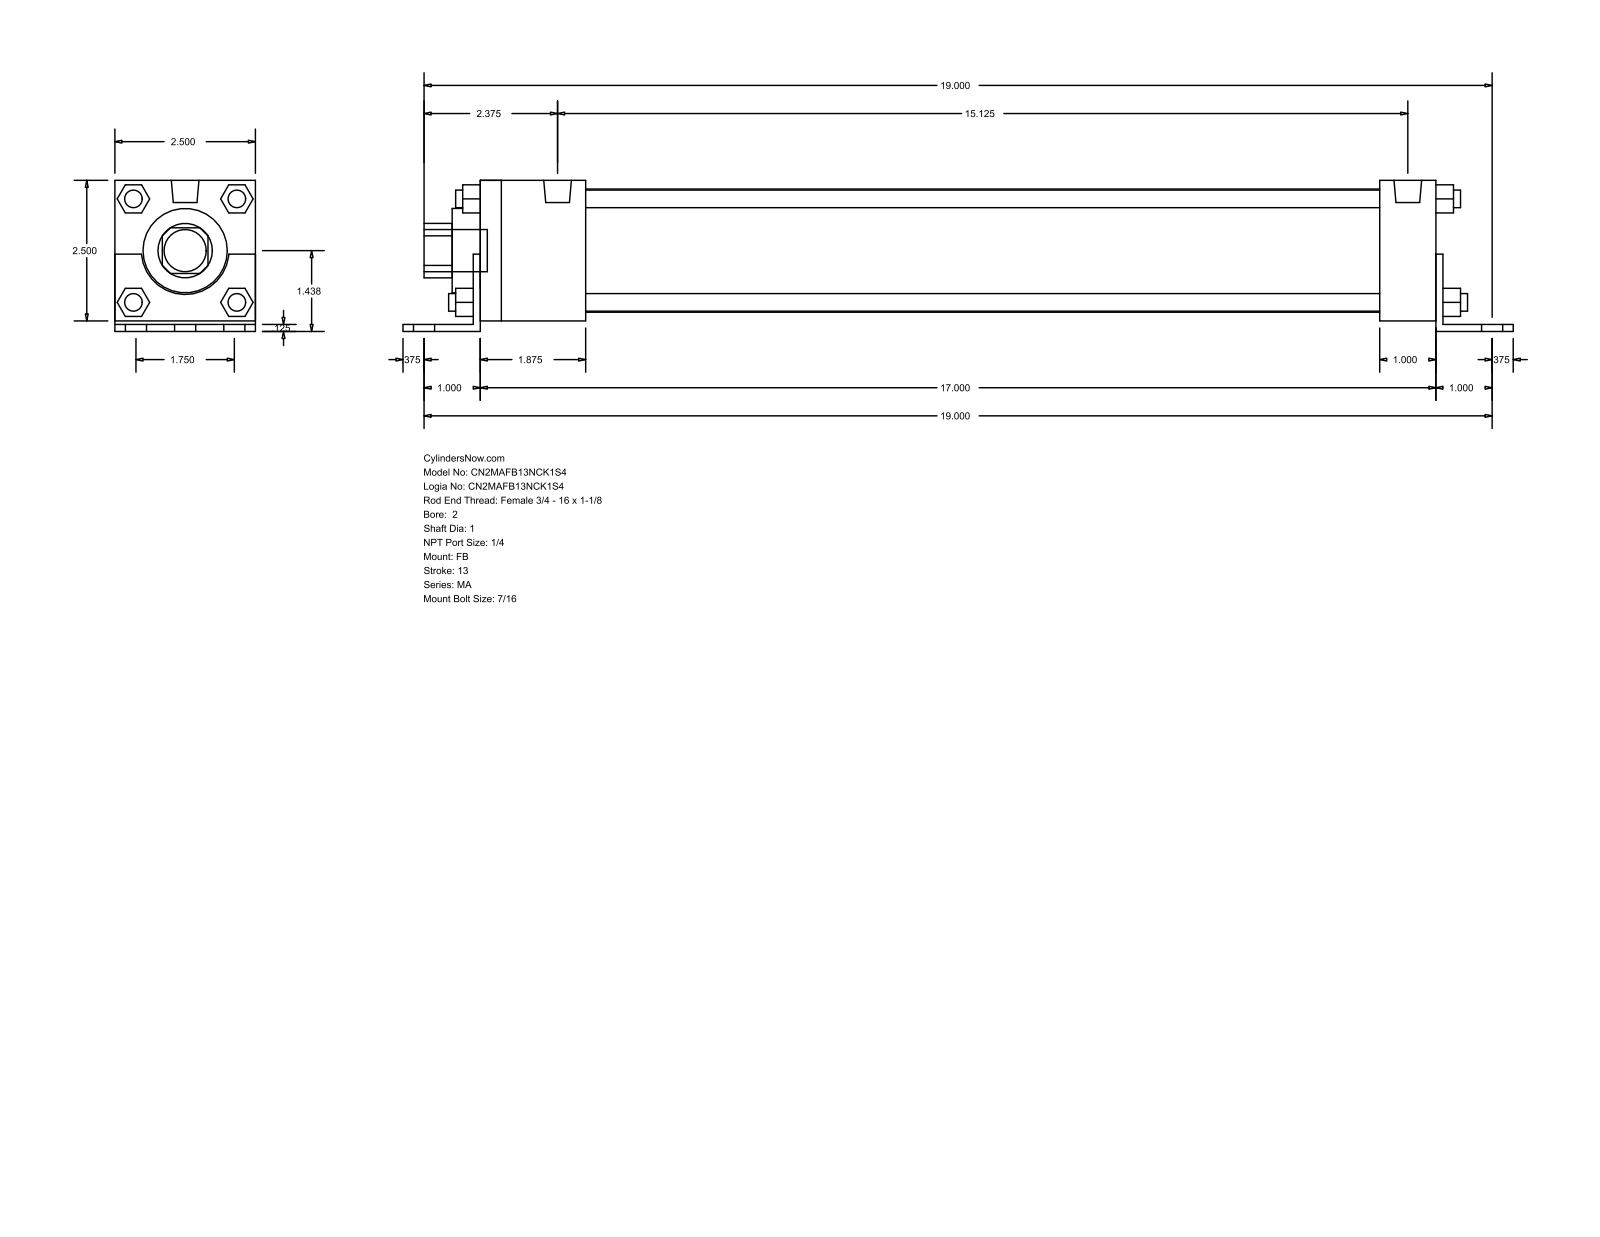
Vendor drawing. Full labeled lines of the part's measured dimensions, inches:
Part name (STEP PRODUCT): MA_FB__0200_1
STEP written by: GSSL Pune (CONFIG_CONTROL_DESIGN)
Units: inches
Bodies: 0 solids, 140 faces (105 planar, 35 cylindrical, 0 other)
Overall size (bounding box): 19.75 × 2.687 × 2.5
Round holes (diameter × count): ⌀1 ×1, ⌀1.5 ×1, ⌀2.19 ×1
Round bosses / shafts (diameter × count): ⌀0.313 ×8, ⌀0.437 ×6, ⌀0.492 ×2, ⌀0.75 ×1
Partial cylindrical surfaces — rounded edges, fillets, slot ends (radius × count): R0.484 ×1, R0.78 ×1
Main face-to-face distances: 2.5, 0.125, 0.187, 2.687, 0.063, 2.563, 0.5, 0.125, 17, 17.125
